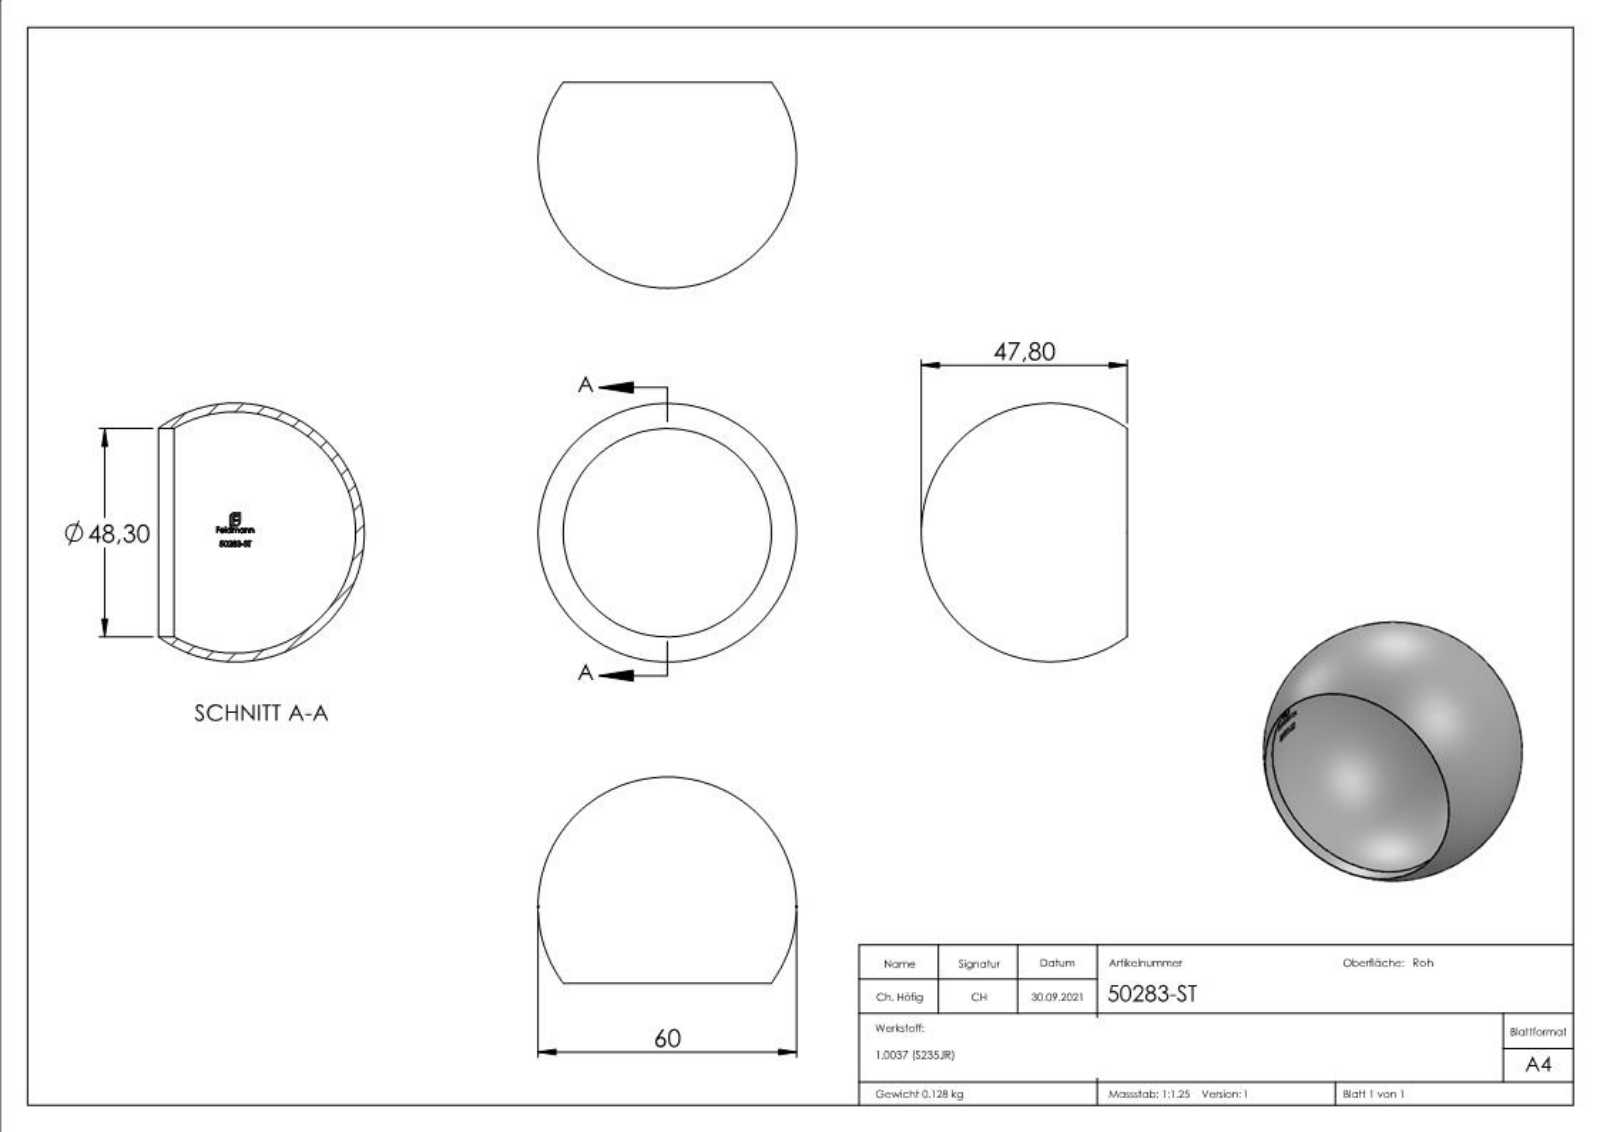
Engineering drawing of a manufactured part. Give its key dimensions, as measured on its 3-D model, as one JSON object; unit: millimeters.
{"part_name": "50283-ST", "step_written_by": "SolidWorks 2018 (CONFIG_CONTROL_DESIGN)", "units": "millimeters", "bodies": {"solids": 1, "faces": 268, "planar": 105, "cylindrical": 1, "other": 162}, "overall_size": [60, 60, 47.8], "volume_mm3": 16422, "surface_area_mm2": 16991, "round_holes": [[48.3, 1]], "face_to_face_distances": [3.21, 3.27, 0.34, 3.66, 4.25, 2.02, 1.01, 1.32, 1.14, 7.52]}
